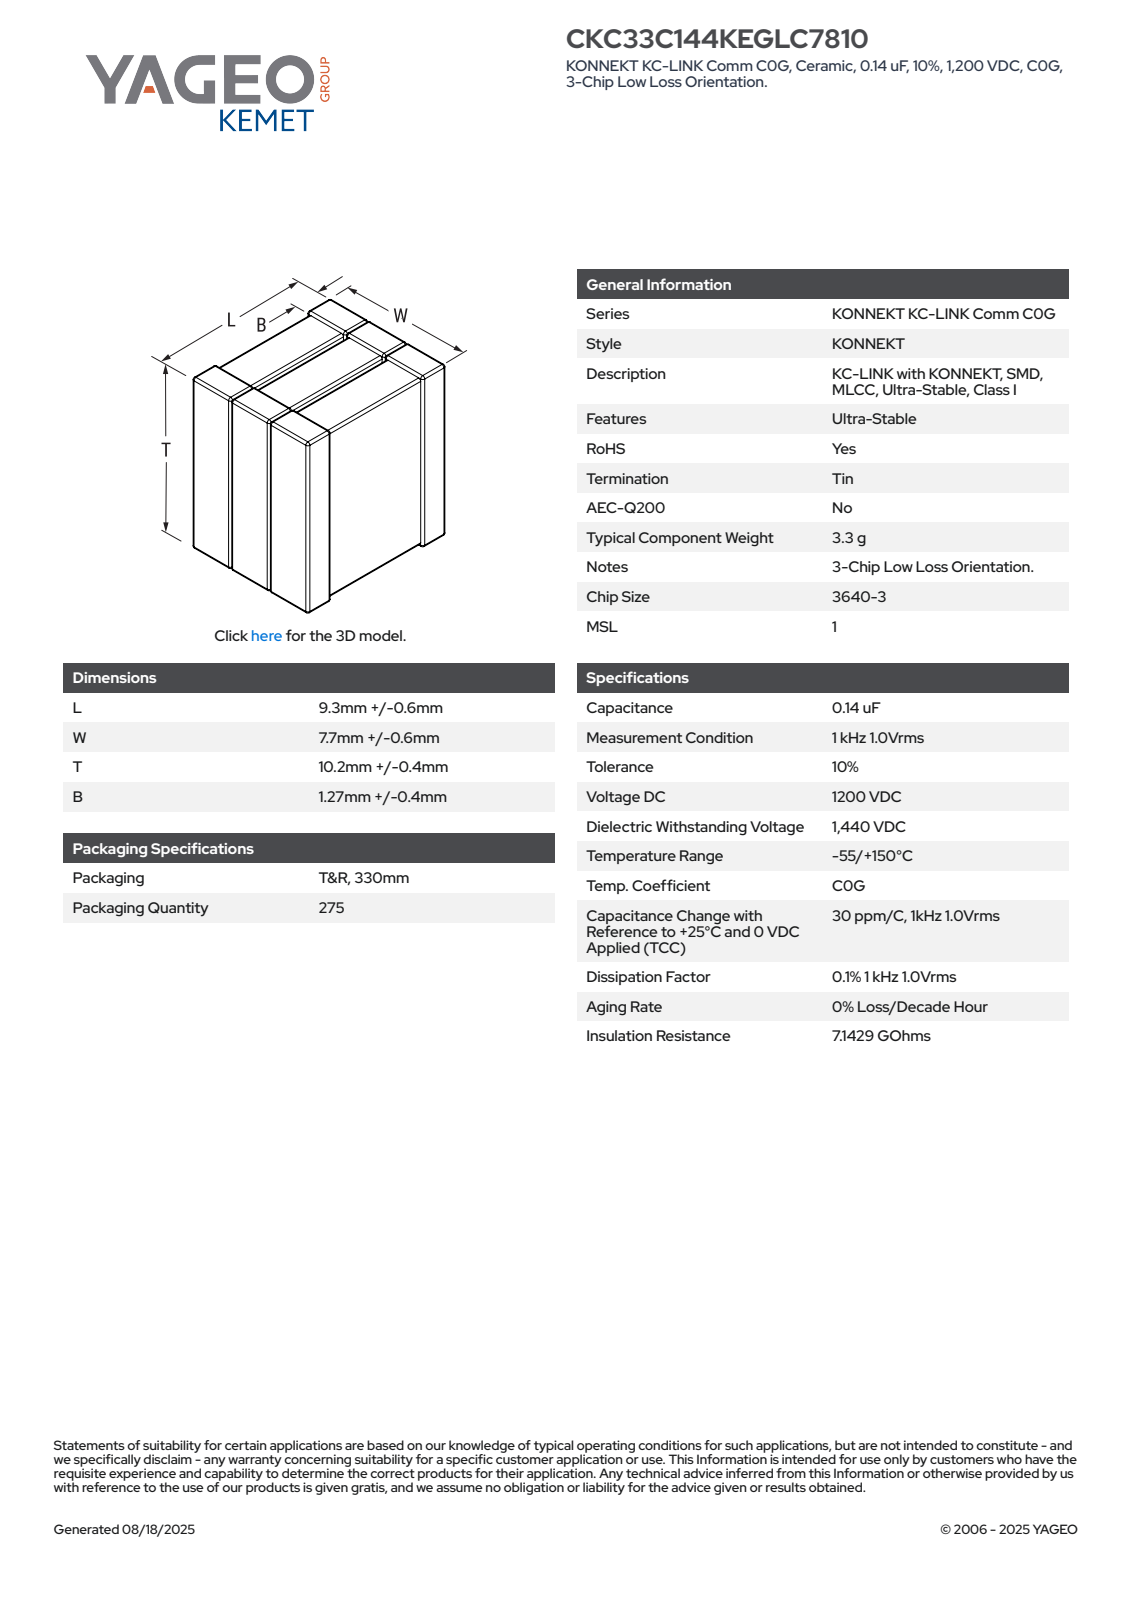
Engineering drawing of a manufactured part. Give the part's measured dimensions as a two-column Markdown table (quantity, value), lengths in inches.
| quantity | value |
| --- | --- |
| part name | CCSS_K3LL_3640_L9.9W8.3B1.67T10.6 |
| STEP written by | SolidWorks 2021 (AUTOMOTIVE_DESIGN) |
| units | inches |
| bodies | 12 solids, 351 faces (213 planar, 90 cylindrical, 48 other) |
| overall size | 0.417 × 0.39 × 0.327 |
| volume | 0.049 in³ |
| surface area | 1.5 in² |
| partial cylindrical surfaces (radius × count) | 0.006 × 56 |
| main face-to-face distances | 0.109, 0.098, 0.103, 0.115, 0.212, 0.207, 0.218, 0.104, 0.39, 0.316 |
